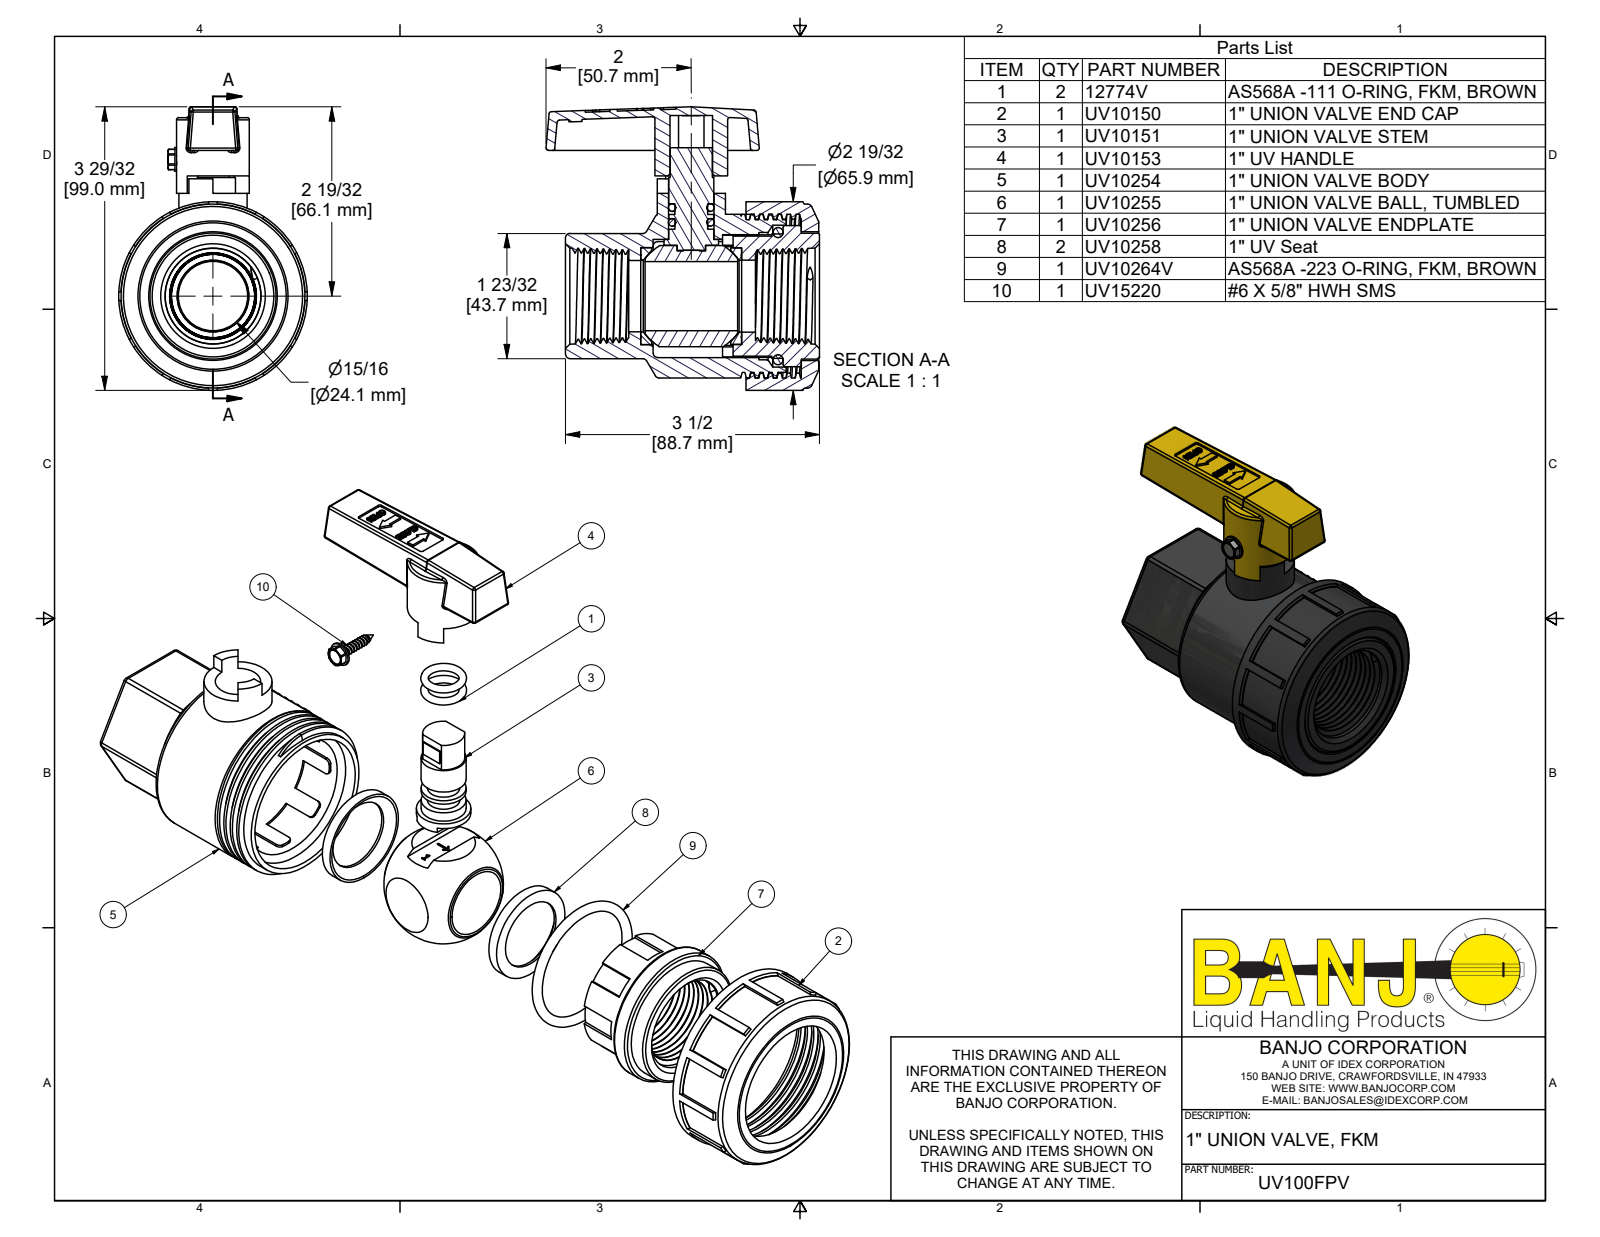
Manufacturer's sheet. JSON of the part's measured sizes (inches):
{"part_name": "UV100FPV; 12774V; UV10255; UV10255M (+8 more)", "step_written_by": "Autodesk Inventor 2019 (AUTOMOTIVE_DESIGN)", "units": "inches", "bodies": {"solids": 14, "faces": 2488, "planar": 1206, "cylindrical": 379, "other": 903}, "overall_size": [22.555, 3.899, 2.594], "volume_in3": 10.16, "surface_area_in2": 211.2, "round_holes": [[0.585, 1], [0.625, 1], [0.95, 1], [0.98, 1], [0.985, 1], [0.99, 1], [1.35, 1], [1.355, 1], [1.69, 1], [1.75, 1], [1.77, 1], [1.98, 1]], "round_bosses_or_shafts": [[2.594, 1], [2.53, 1], [2.25, 1], [2.097, 1], [1.94, 1], [1.73, 1], [1.71, 1], [1.33, 1]], "partial_cylinders_radius": [[0.03, 44], [0.06, 28], [0.125, 3], [0.139, 1], [0.29, 1], [0.393, 1], [0.396, 1], [0.516, 1]], "face_to_face_distances": [1.72, 0.12, 0.25, 0.75, 0.165, 0.084, 0.834, 1, 0.59, 0.5], "hole_center_spacings": [1.73]}
